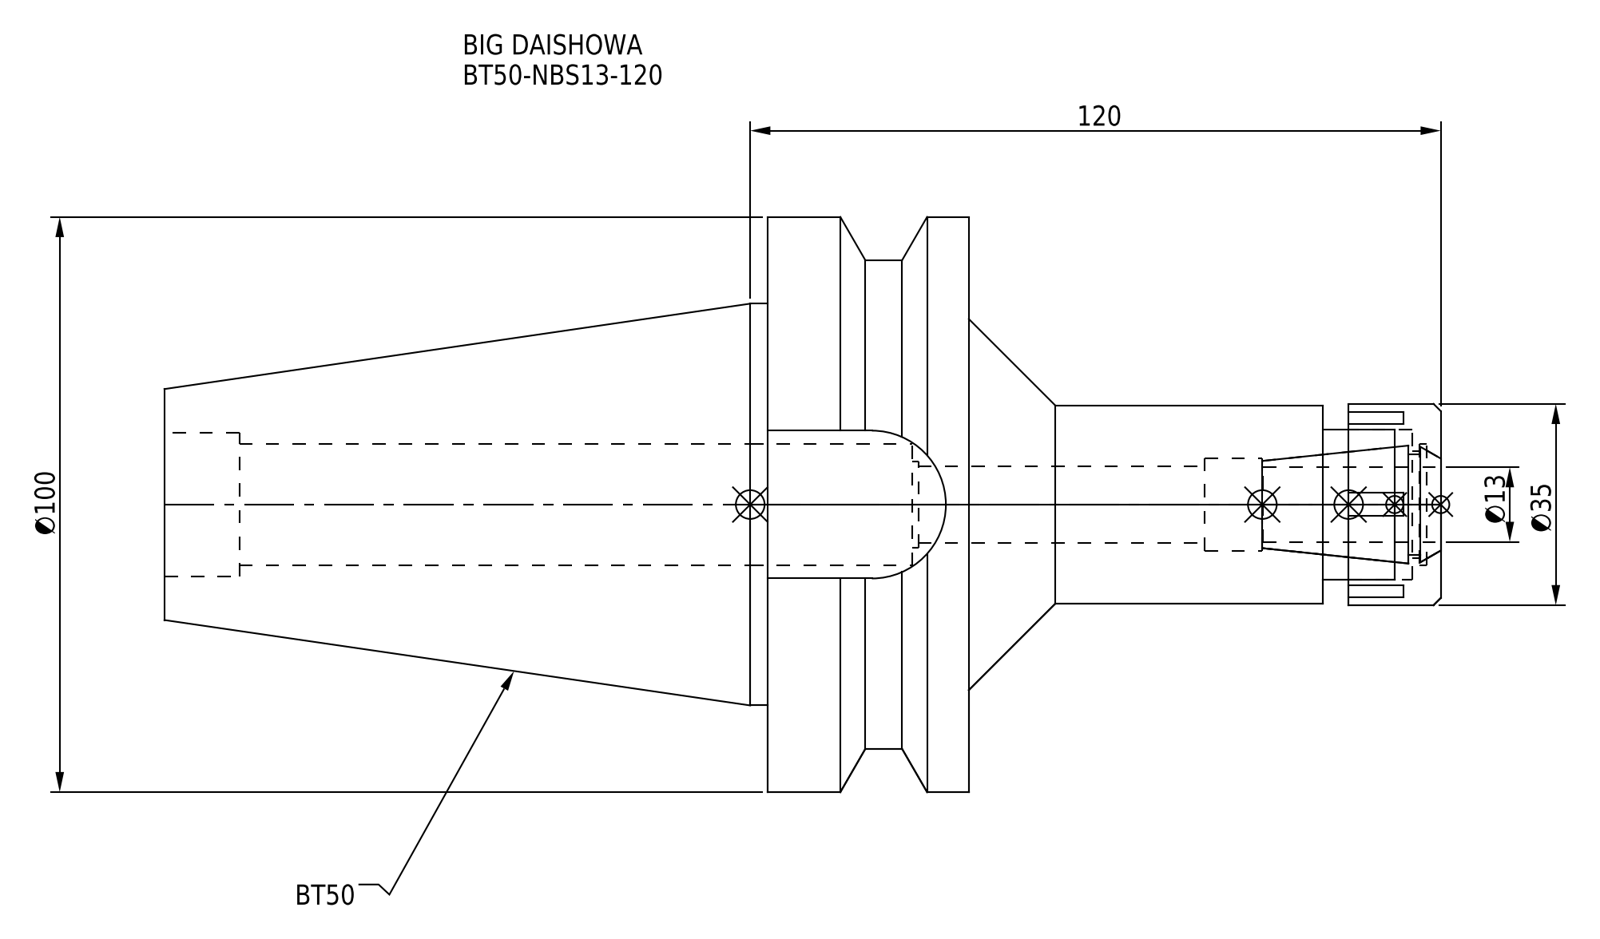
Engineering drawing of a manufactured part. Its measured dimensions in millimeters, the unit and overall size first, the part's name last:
Units: millimetres
Overall size (bounding box): 221.8 × 100 × 100
Round holes (diameter × count): ⌀13.3 ×1, ⌀15 ×1, ⌀16 ×1, ⌀18.5 ×1, ⌀21 ×1, ⌀21.2 ×1, ⌀25 ×1, ⌀26 ×1
Round bosses / shafts (diameter × count): ⌀100 ×1, ⌀85 ×1, ⌀69.85 ×1, ⌀35 ×1, ⌀34.5 ×1
Partial cylindrical surfaces — rounded edges, fillets, slot ends (radius × count): R12.85 ×1
Main face-to-face distances: 35, 139.8, 104.8, 117, 70.8, 82, 221.8, 20.5, 8, 25.7
Volume: 519 025 mm³ · Surface area: 69 272 mm²
Bodies: 2 solids, 93 faces (45 planar, 34 cylindrical, 14 other)
Part name (STEP PRODUCT): DXF_TEMP_ASSY_ASM_4_ASM.stp; NBN13_1.stp; BT50-NBS13-120_1.stp; BT50NB13120-130_ASM.stp (+3 more)
STEP written by: SolidWorks 2019 (CONFIG_CONTROL_DESIGN)
